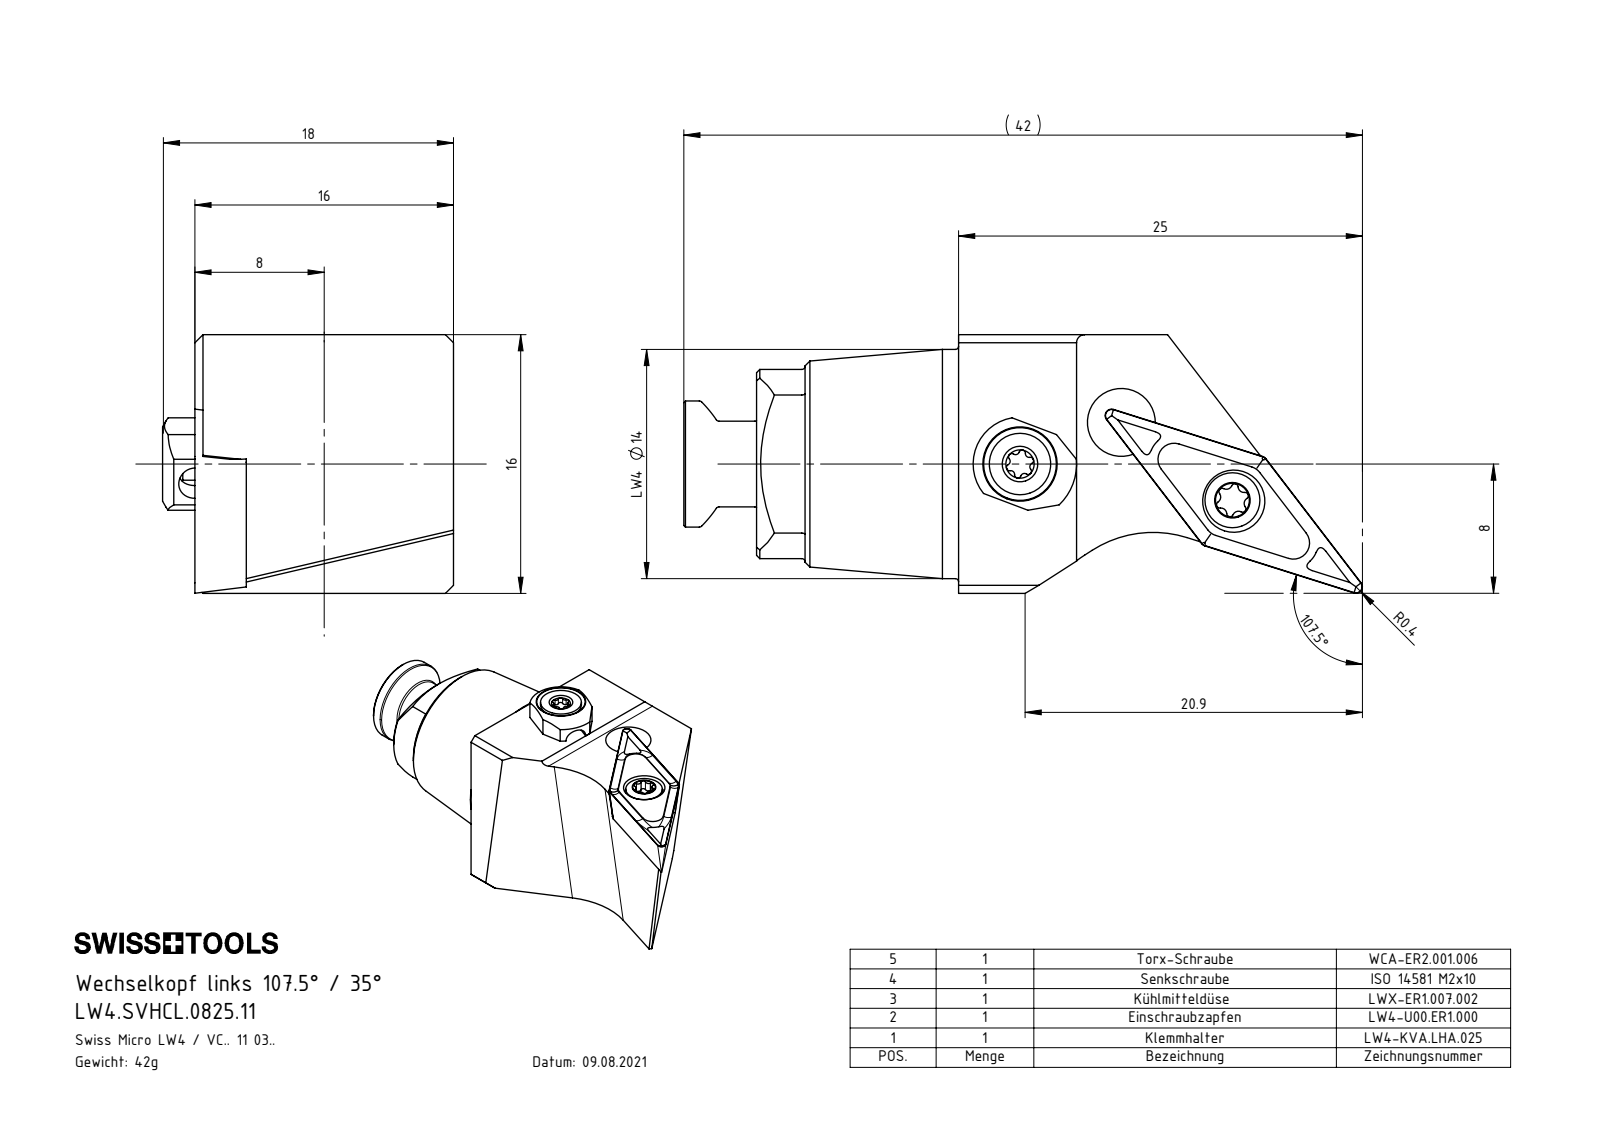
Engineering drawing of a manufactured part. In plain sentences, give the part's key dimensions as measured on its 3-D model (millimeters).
The part is named "VCGT110304; LW4-U00.ER1.000_B; LW4-KVA.LHA.025_A; LWX-ER1.007.002 (+3 more)". Its 3-D file was written by "SolidWorks 2022 (CONFIG_CONTROL_DESIGN)". It is 6 solids with 260 faces: 70 planar, 82 cylindrical and 108 other. Overall it measures 41.99 by 18 by 16 millimeters. Its volume is 5 206 cubic millimeters and its surface area 3 345 square millimeters. Round holes: 2 of diameter 2, 1 of diameter 1.6, 1 of diameter 2.05, 1 of diameter 2.5, 1 of diameter 2.8, 1 of diameter 3, 1 of diameter 3.85, 1 of diameter 4.2, 1 of diameter 5.5. Round bosses or shafts: 1 of diameter 14.17, 1 of diameter 7.7, 1 of diameter 6, 1 of diameter 5.3, 1 of diameter 5, 1 of diameter 3.8, 1 of diameter 3.4, 1 of diameter 2.5. Partial cylindrical surfaces (rounded edges, fillets, slot ends): 8 of radius 0.2, 6 of radius 0.21, 6 of radius 0.24, 4 of radius 0.36, 2 of radius 0.36, 1 of radius 0.5, 1 of radius 1, 1 of radius 2.9. The main face-to-face distances are 16, 12.82, 3.18, 15.5, 2.68, 0.5, 7.5, 2, 12.5, 4. The hole center spacings are 5.86, 8.39, 8.49, 10.54, 10.63.
